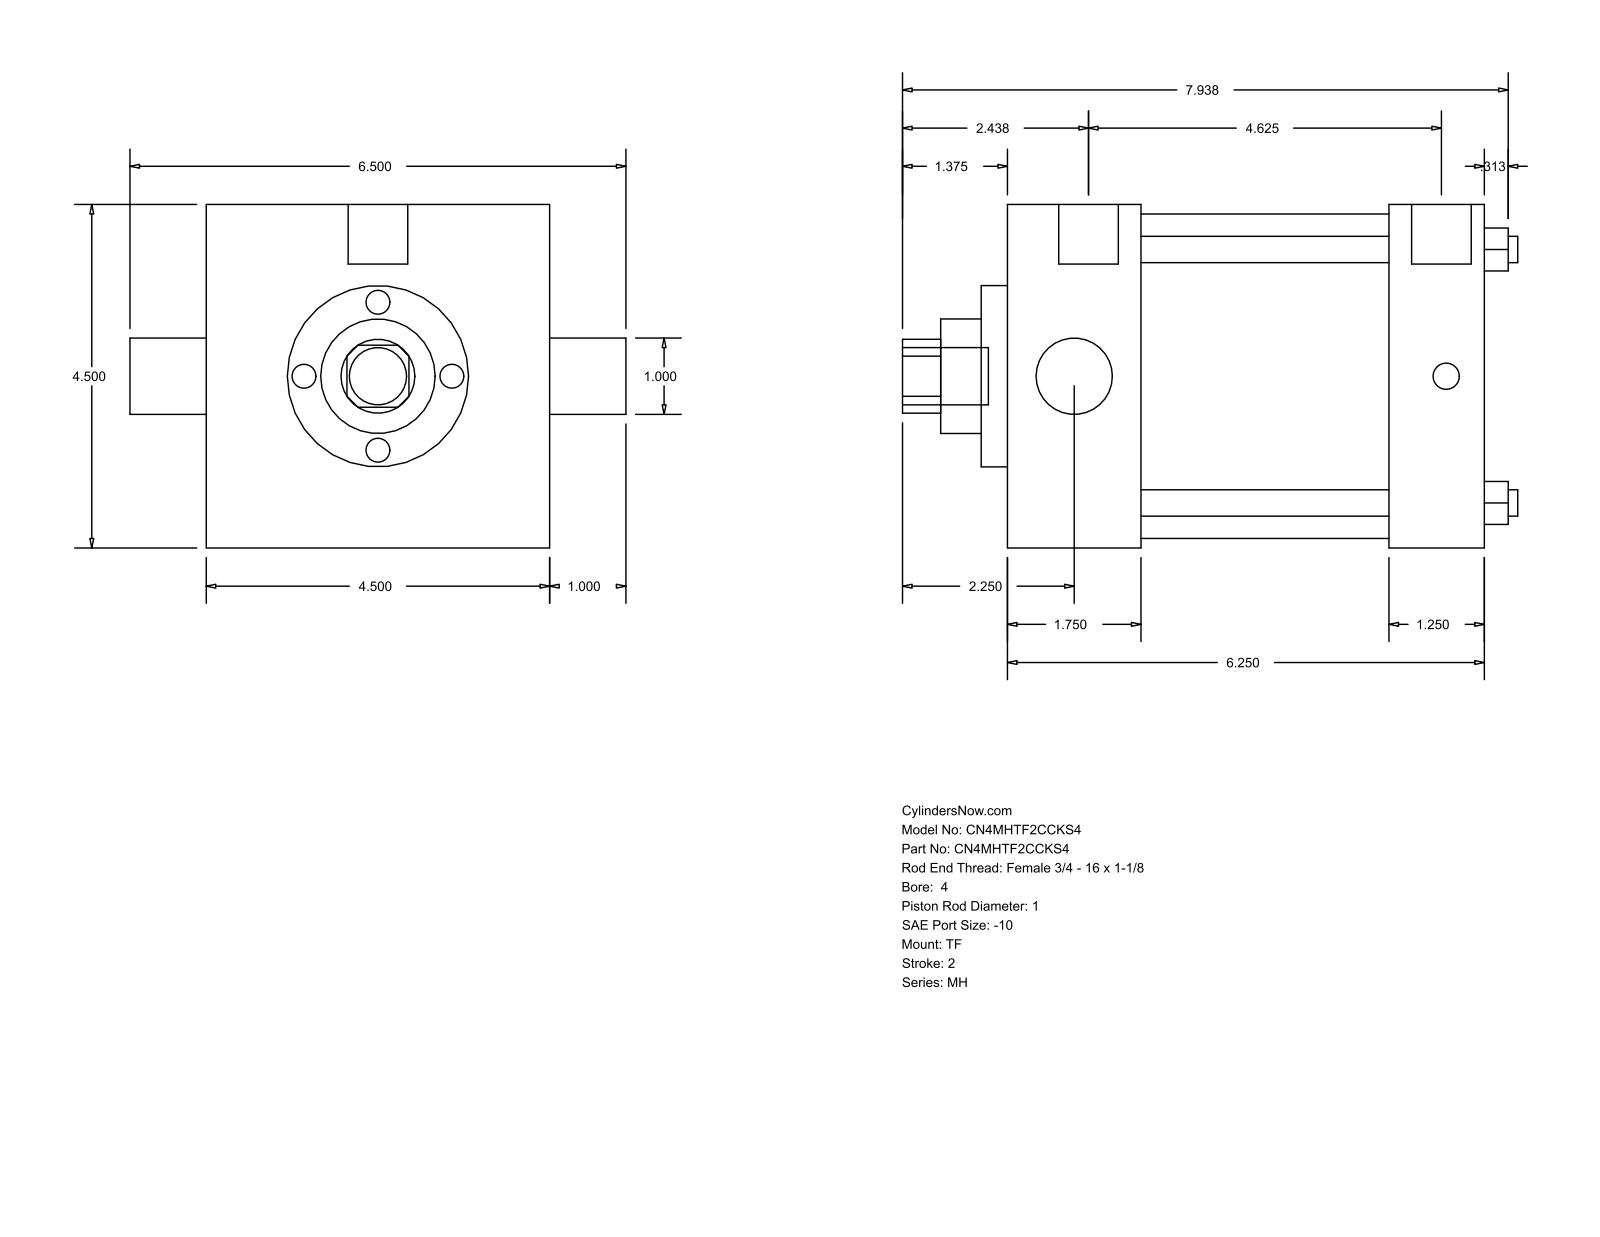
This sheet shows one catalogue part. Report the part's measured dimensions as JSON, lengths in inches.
{"part_name": "MH_TF__0400_1", "step_written_by": "GSSL Pune (CONFIG_CONTROL_DESIGN)", "units": "inches", "bodies": {"solids": 0, "faces": 86, "planar": 61, "cylindrical": 25, "other": 0}, "overall_size": [8.063, 6.5, 4.5], "round_holes": [[0.345, 4], [1, 2], [1.5, 1], [2.375, 1], [4.25, 1]], "round_bosses_or_shafts": [[0.344, 3], [0.781, 2], [0.75, 1]], "partial_cylinders_radius": [[0.484, 1]], "face_to_face_distances": [4.5, 6.25, 1.75, 5, 3.25, 1.25, 0.344, 2.094, 5.344, 6.594], "hole_center_spacings": [2.347, 3.32, 4.695]}
